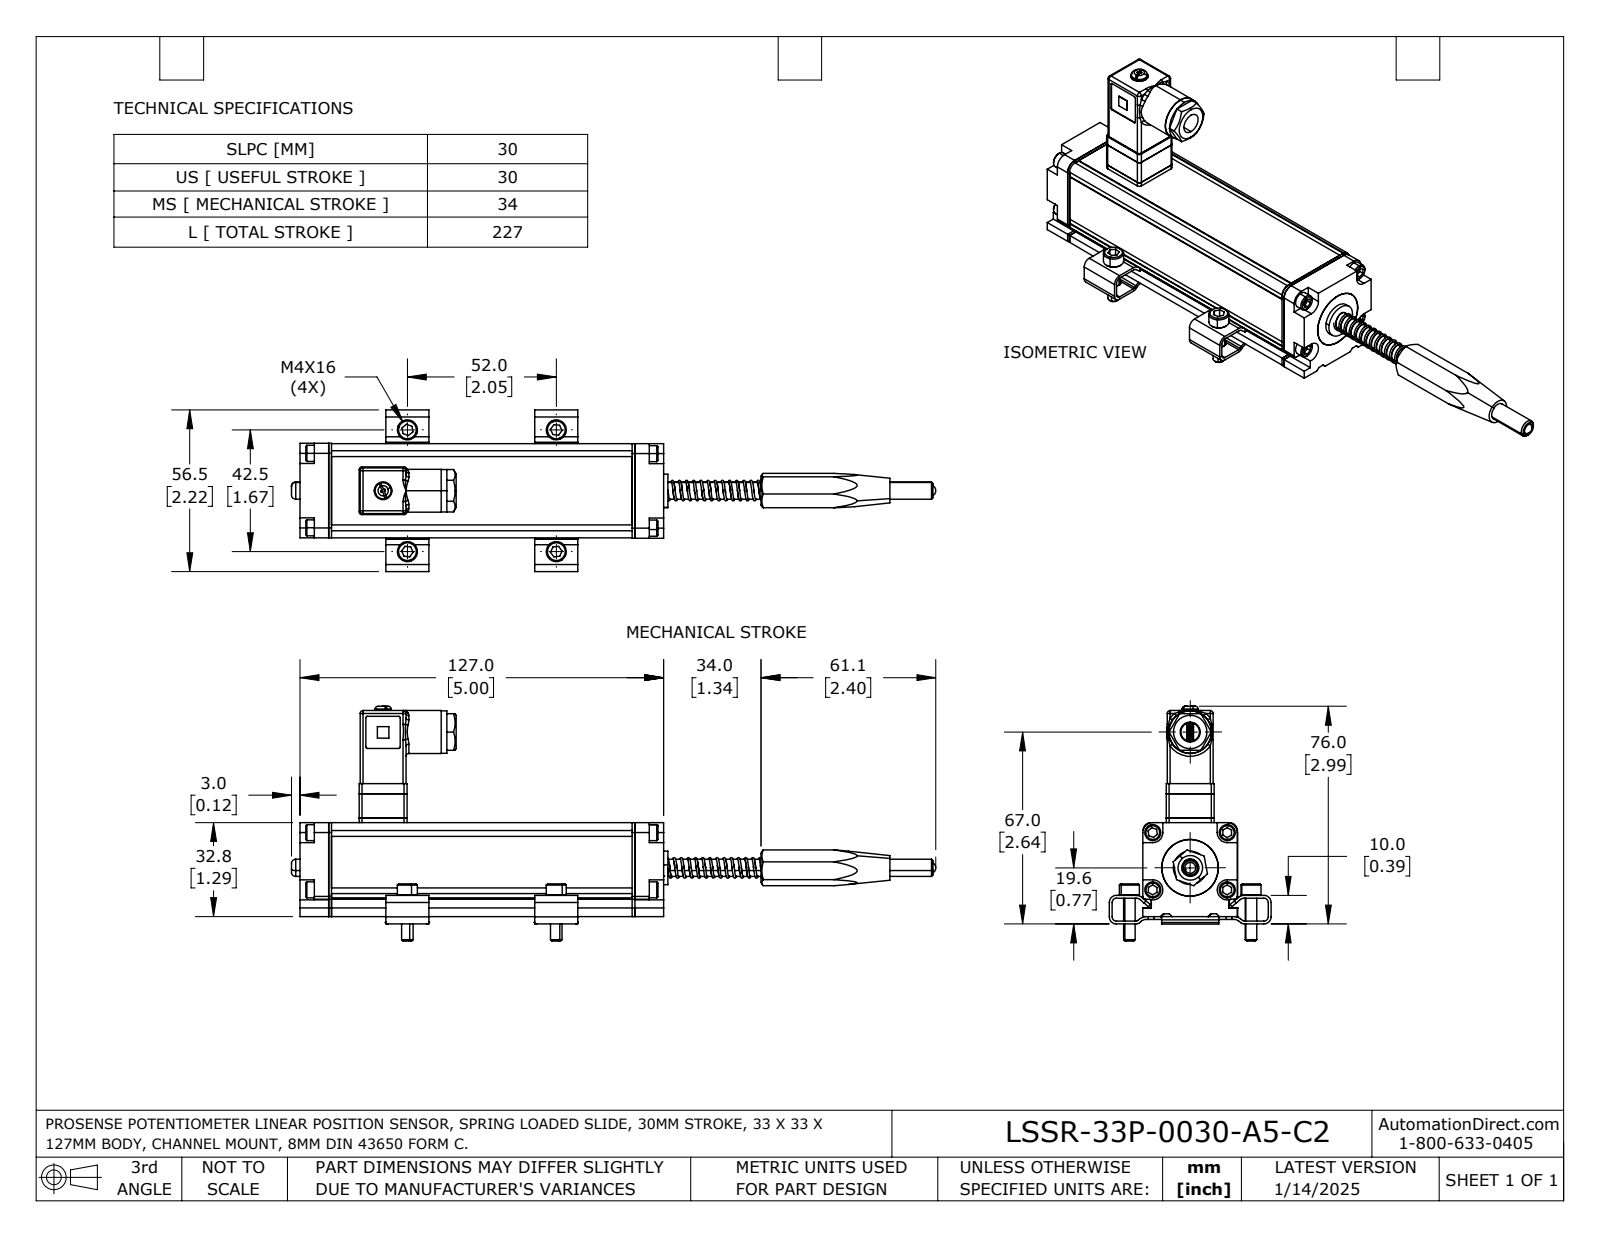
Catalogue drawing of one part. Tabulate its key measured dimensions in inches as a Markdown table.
| quantity | value |
| --- | --- |
| part name | LSSR-33P-0030-A5-C2 |
| STEP written by | SolidWorks 2024 (AUTOMOTIVE_DESIGN) |
| units | inches |
| bodies | 34 solids, 1392 faces (671 planar, 569 cylindrical, 152 other) |
| overall size | 8.86 × 3.228 × 2.224 |
| volume | 9.114 in³ |
| surface area | 94.97 in² |
| round holes (diameter × count) | 0.114 × 16, 0.138 × 8, 0.142 × 8, 0.055 × 4, 0.091 × 4, 0.197 × 4, 0.709 × 4, 0.244 × 3, 0.079 × 2, 0.11 × 2, 0.154 × 2, 0.268 × 2 |
| round bosses / shafts (diameter × count) | 0.079 × 16, 0.22 × 9, 0.118 × 8, 0.276 × 4, 0.157 × 4, 0.776 × 2, 0.503 × 2, 0.177 × 2 |
| partial cylindrical surfaces (radius × count) | 0.039 × 32, 0.079 × 20, 0.051 × 8, 0.059 × 8, 0.089 × 8, 0.118 × 8, 0.138 × 8, 0.02 × 6 |
| main face-to-face distances | 0.039, 4.173, 1.291, 0.118, 1.295, 0.394, 0.433, 0.079, 0.354, 4.606 |
| hole center spacings | 0.343, 0.546, 0.583, 0.786, 1.063, 1.024, 1.067, 0.204 |
